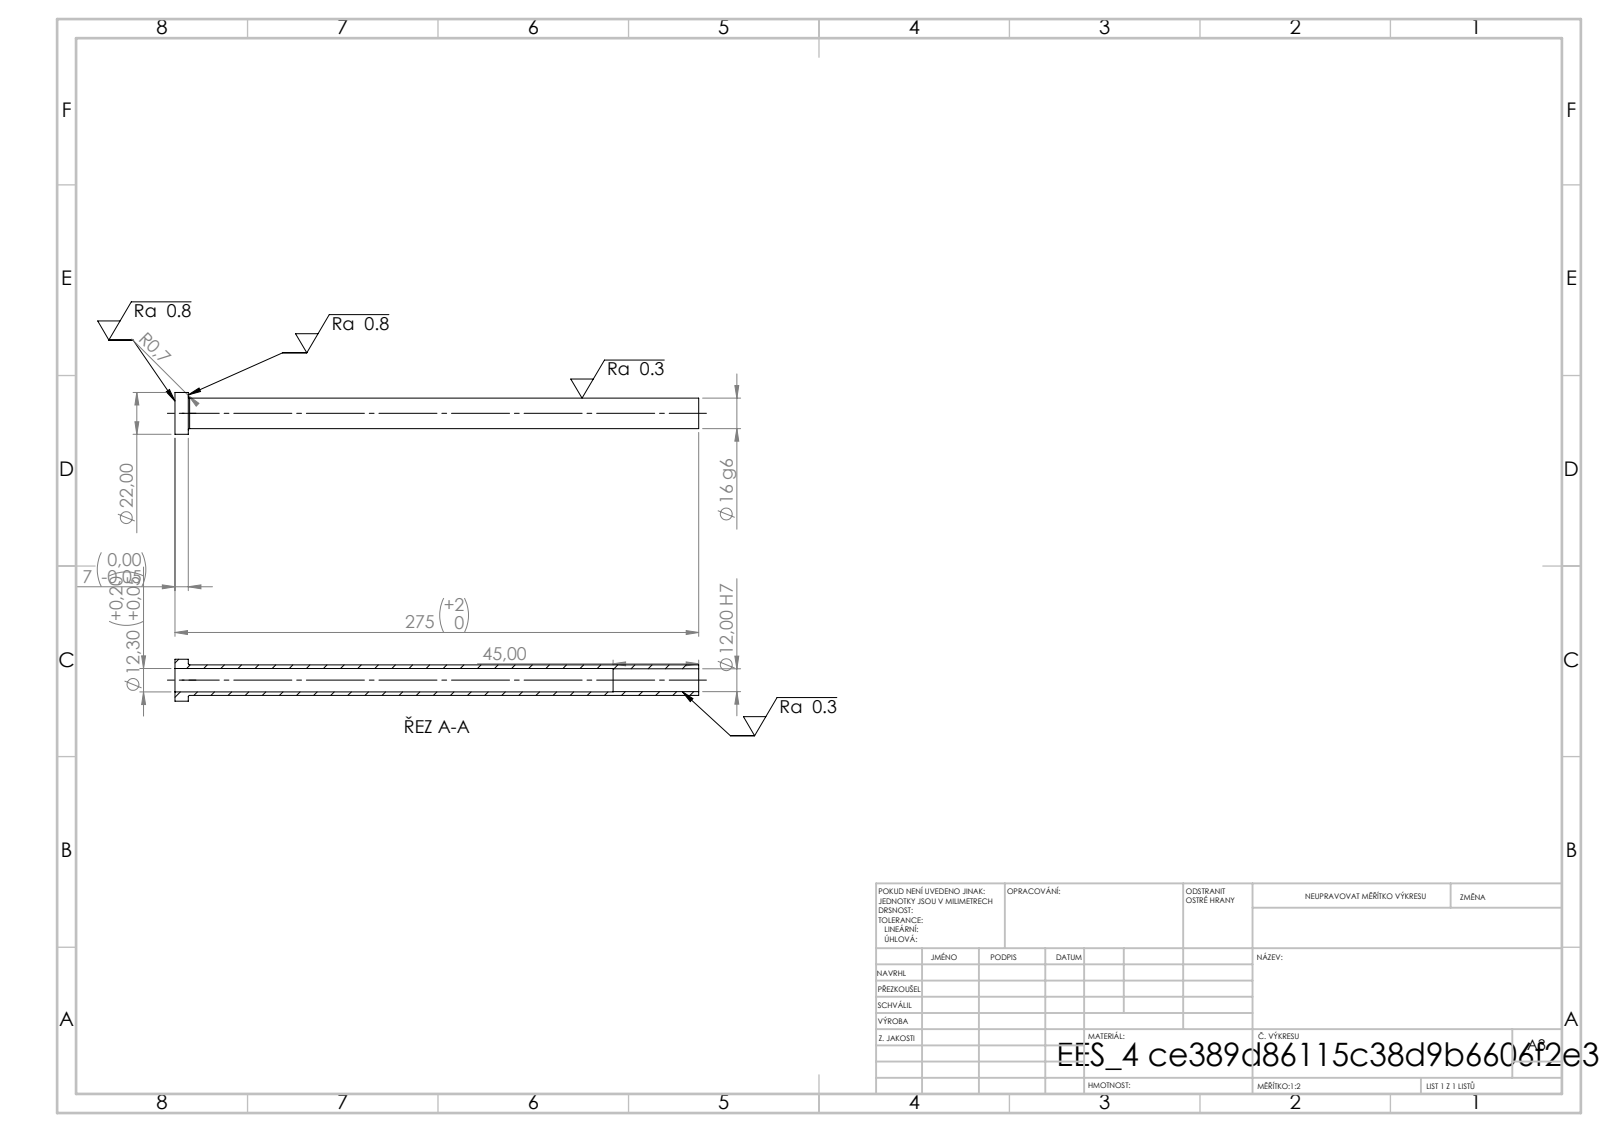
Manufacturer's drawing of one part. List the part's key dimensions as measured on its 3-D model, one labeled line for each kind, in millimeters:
STEP written by: SolidWorks 2019 (CONFIG_CONTROL_DESIGN)
Units: millimetres
Bodies: 1 solid, 14 faces (4 planar, 8 cylindrical, 2 other)
Overall size (bounding box): 275 × 22 × 22
Volume: 24 132 mm³ · Surface area: 25 058 mm²
Round holes (diameter × count): ⌀12 ×1, ⌀12.3 ×1
Round bosses / shafts (diameter × count): ⌀22 ×1, ⌀16 ×1
Main face-to-face distances: 7, 275, 268, 230, 223, 45
